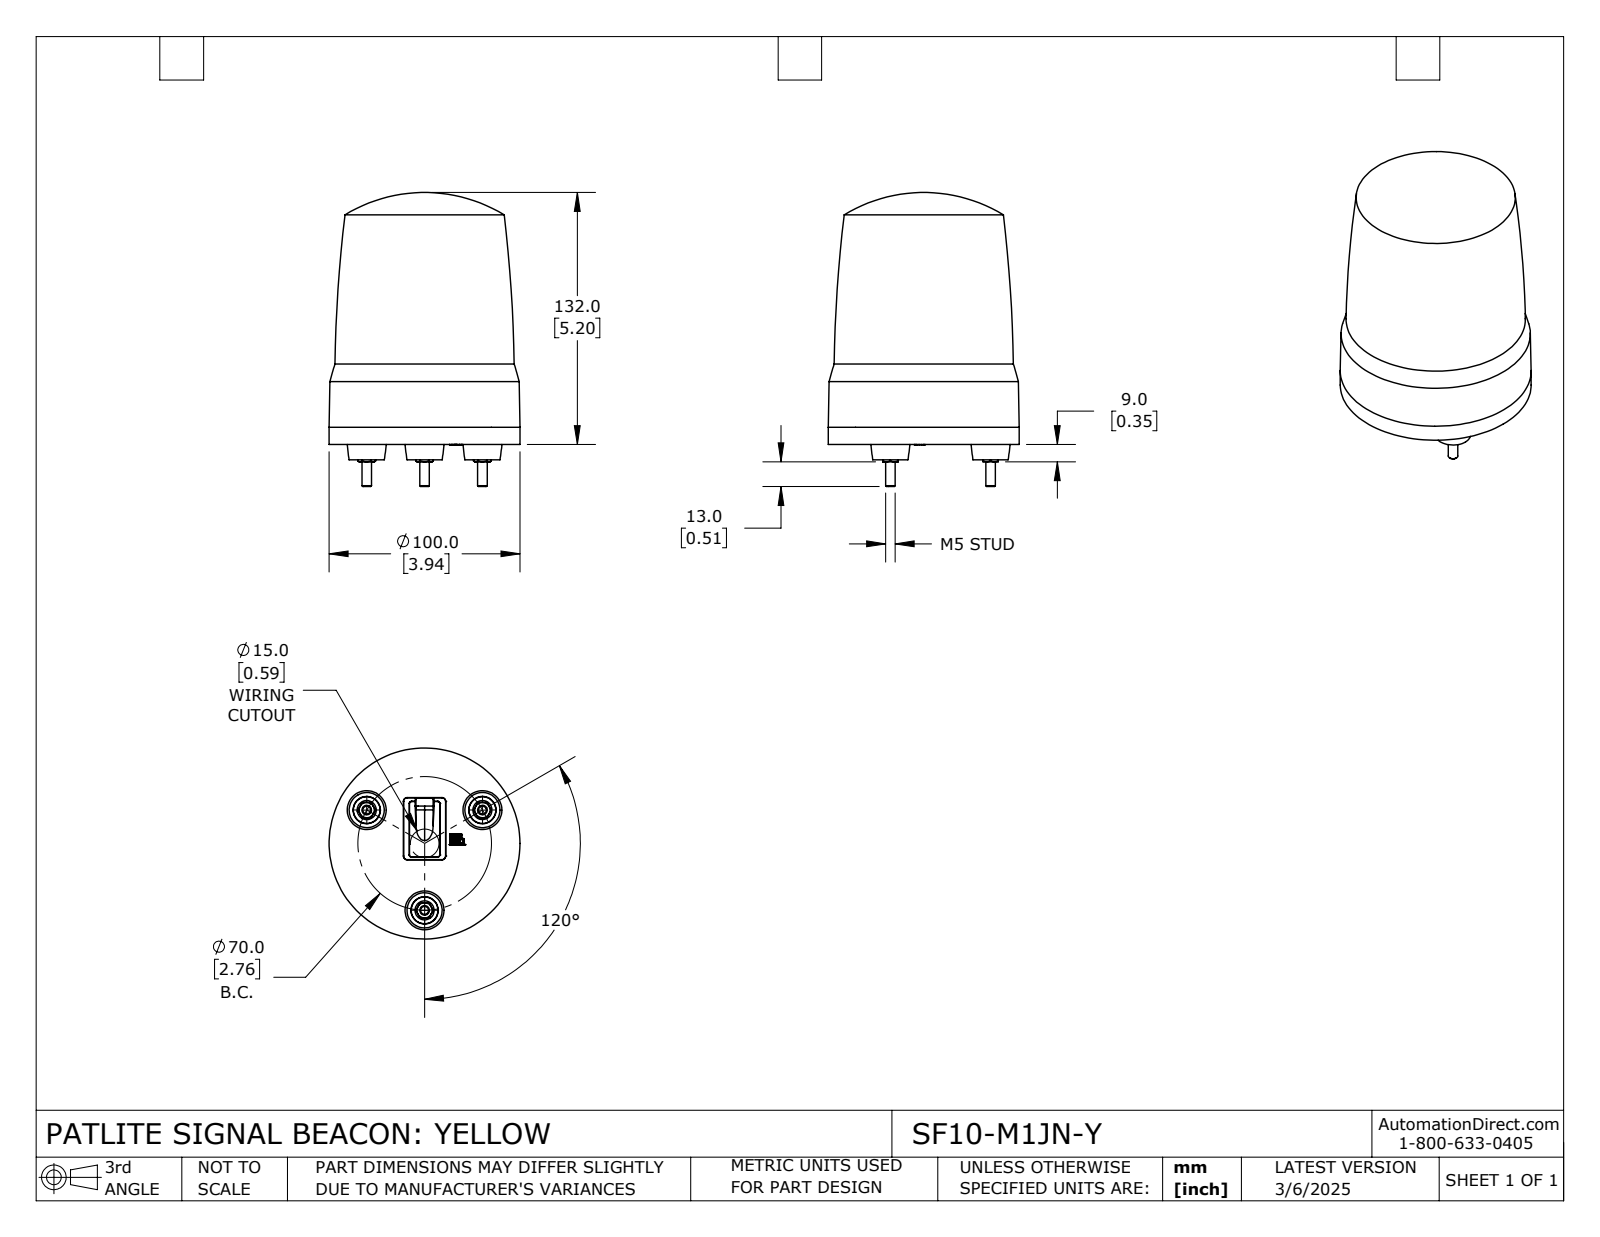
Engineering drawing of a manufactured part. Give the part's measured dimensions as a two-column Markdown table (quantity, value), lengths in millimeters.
| quantity | value |
| --- | --- |
| part name | SF10-M1JN-Y |
| STEP written by | SolidWorks 2024 (CONFIG_CONTROL_DESIGN) |
| units | millimeters |
| bodies | 1 solid, 327 faces (159 planar, 14 cylindrical, 154 other) |
| overall size | 154 × 100 × 100 |
| volume | 859 960 mm³ |
| surface area | 52 586 mm² |
| round bosses / shafts (diameter × count) | 10 × 3, 5 × 3, 100 × 1 |
| main face-to-face distances | 8, 0.85, 8.85, 1.6, 10.45, 2.45, 3.8, 4.2, 5.05, 6.65 |
